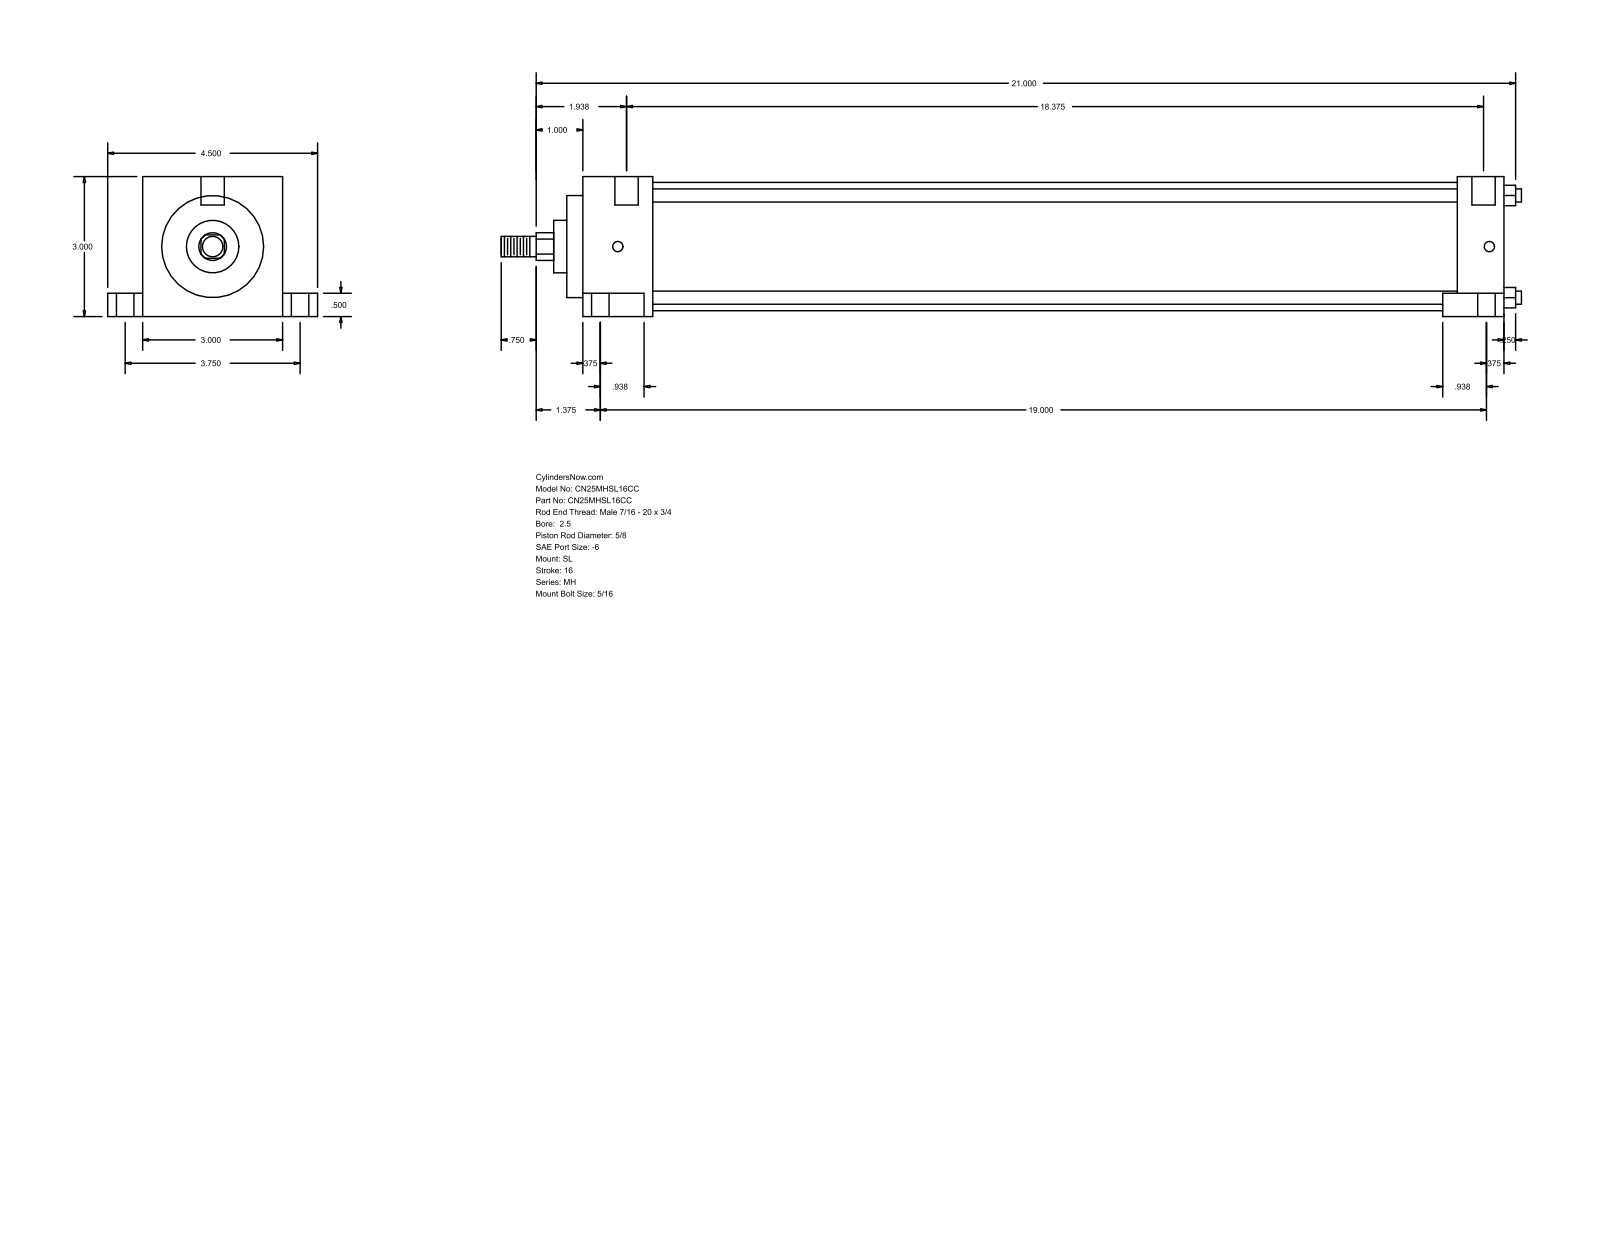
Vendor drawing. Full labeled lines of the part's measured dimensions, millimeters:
Part name (STEP PRODUCT): MH_SL__0250_0.625
STEP written by: GSSL Pune (CONFIG_CONTROL_DESIGN)
Units: millimetres
Bodies: 0 solids, 86 faces (61 planar, 25 cylindrical, 0 other)
Overall size (bounding box): 555.62 × 114.3 × 76.2
Round holes (diameter × count): ⌀5.56 ×2, ⌀9.53 ×2, ⌀15.88 ×2, ⌀12.7 ×1
Round bosses / shafts (diameter × count): ⌀7.14 ×4, ⌀69.85 ×1, ⌀55.55 ×1, ⌀28.57 ×1, ⌀15.88 ×1, ⌀11.11 ×1
Partial cylindrical surfaces — rounded edges, fillets, slot ends (radius × count): R7.54 ×1
Main face-to-face distances: 76.2, 25.4, 484.98, 510.38, 63.5, 12.7, 19.05, 95.25, 31.75, 477.04
Hole centre spacings: 47.65, 3.17, 95.24
